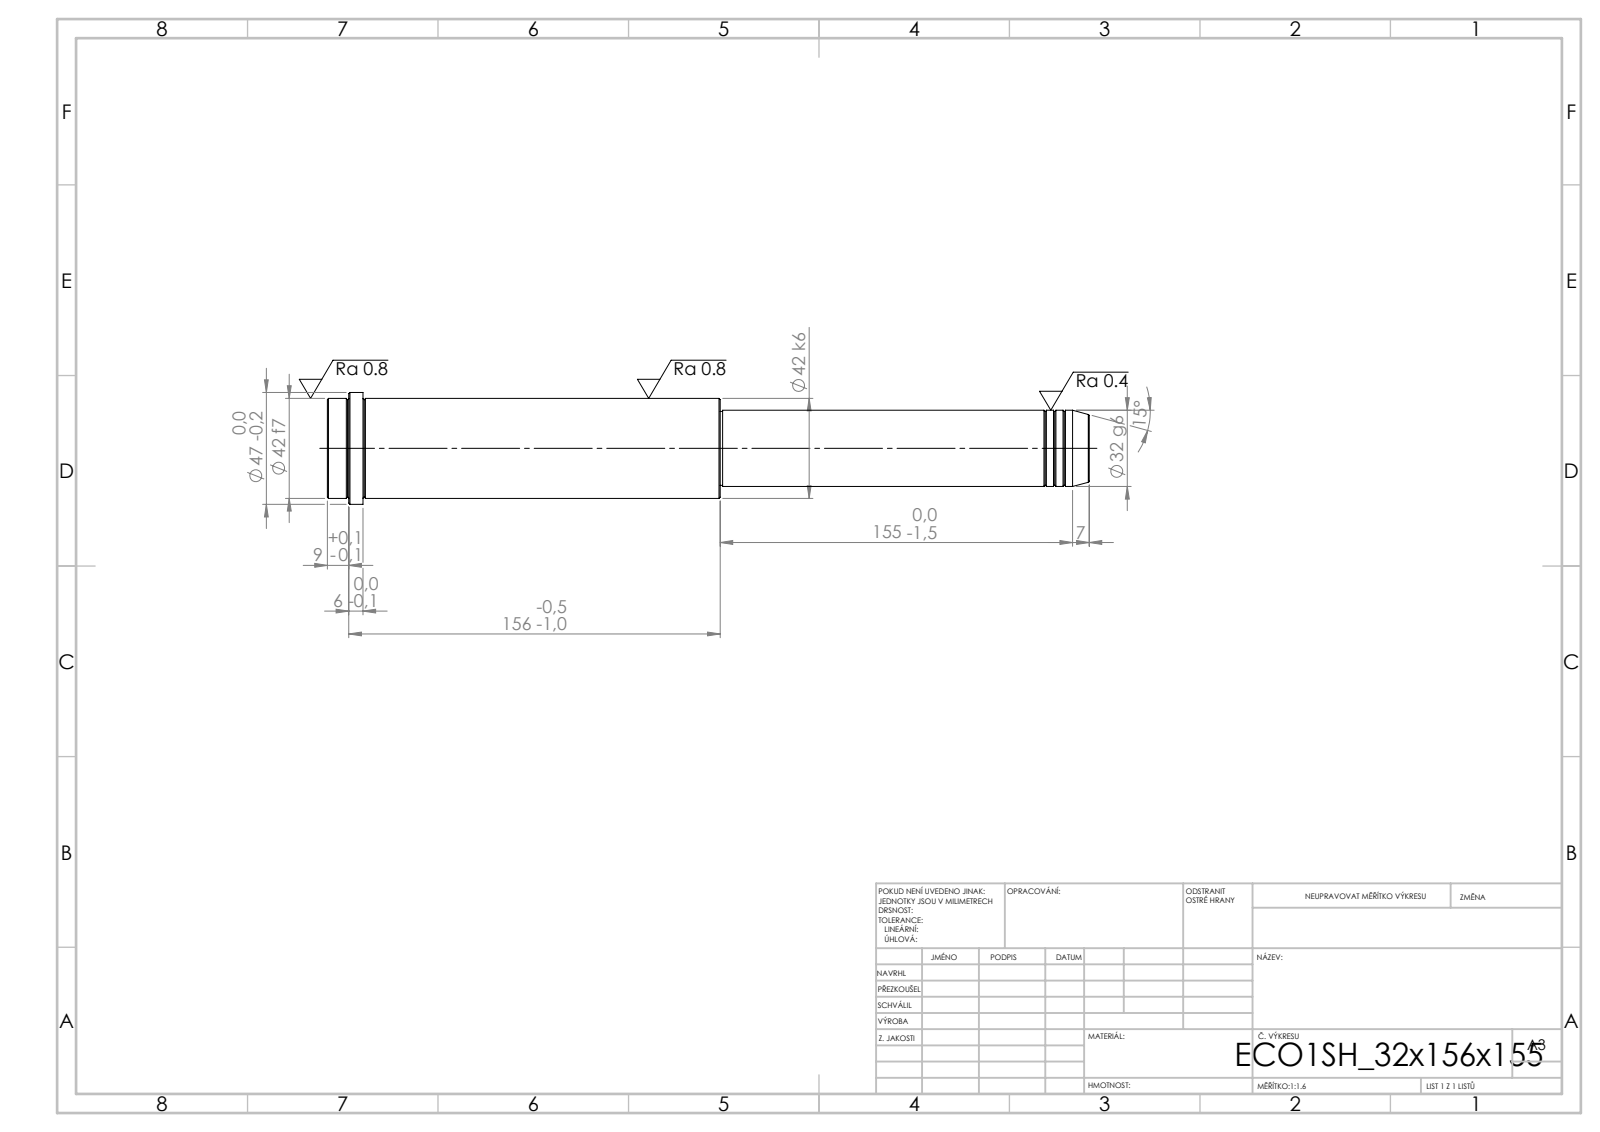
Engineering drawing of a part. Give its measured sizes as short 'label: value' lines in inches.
written by: SolidWorks 2019 (CONFIG_CONTROL_DESIGN)
unit: in
bodies: 1 solid, 52 faces (6 planar, 16 cylindrical, 30 other)
size: 12.598 × 1.85 × 1.85
volume: 21.63 in³; area: 63.54 in²
bosses: 1× ⌀1.85, 1× ⌀1.654, 1× ⌀1.26, 1× ⌀1.22
face distances: 12.598, 6.102, 6.496, 12.008, 5.906, 0.591, 12.244, 6.142, 0.236, 0.354
